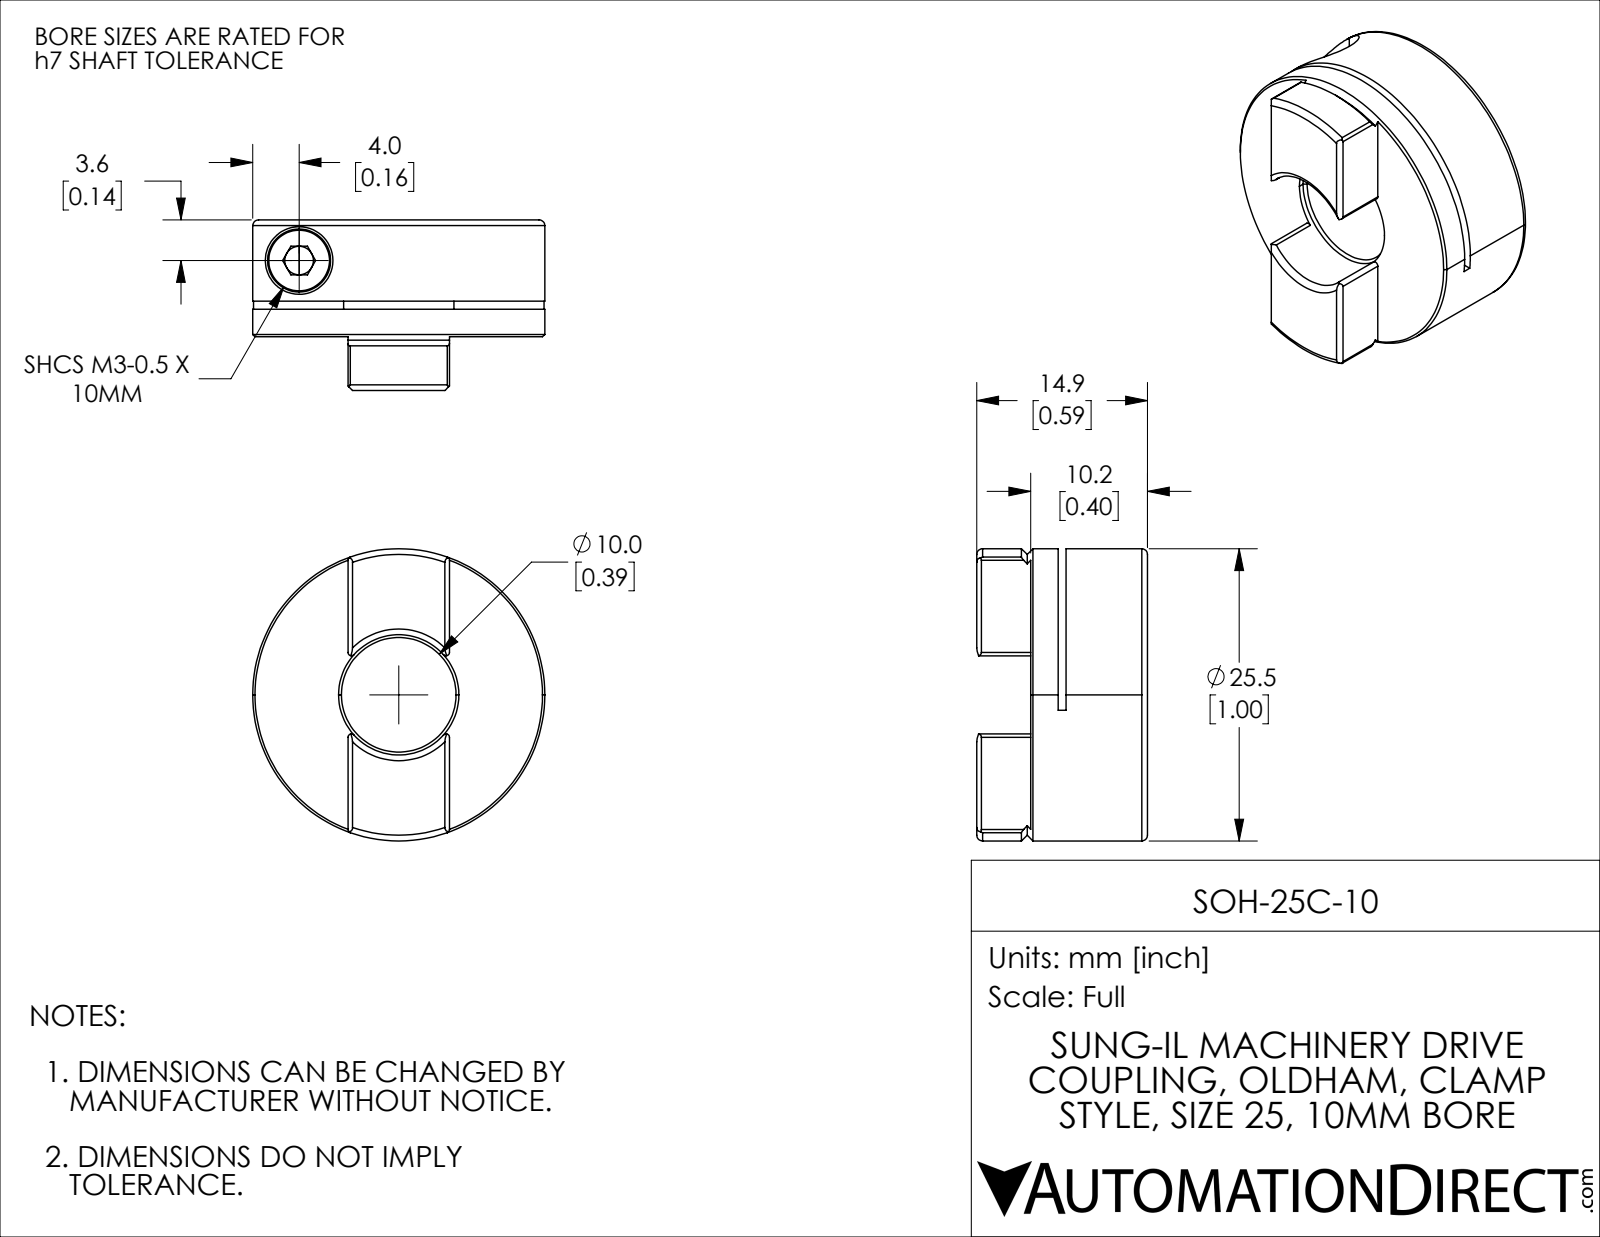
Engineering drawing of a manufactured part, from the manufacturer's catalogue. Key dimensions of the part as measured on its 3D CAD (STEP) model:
Part name (STEP PRODUCT): SOH-25C-10
STEP written by: SolidWorks 2021 (CONFIG_CONTROL_DESIGN)
Units: millimetres
Bodies: 2 solids, 96 faces (38 planar, 33 cylindrical, 25 other)
Overall size (bounding box): 25.5 × 25.5 × 14.9
Volume: 4 718 mm³ · Surface area: 3 222 mm²
Round holes (diameter × count): ⌀2.5 ×1, ⌀3.3 ×1, ⌀5.9 ×1, ⌀10 ×1, ⌀10.5 ×1
Round bosses / shafts (diameter × count): ⌀25.5 ×1, ⌀5.5 ×1, ⌀3 ×1
Partial cylindrical surfaces — rounded edges, fillets, slot ends (radius × count): R0.3 ×8, R22.5 ×1
Main face-to-face distances: 7.8, 7.1, 10.2, 2.4, 0.7, 3.1, 14.9, 4.7, 8.86, 0.8
